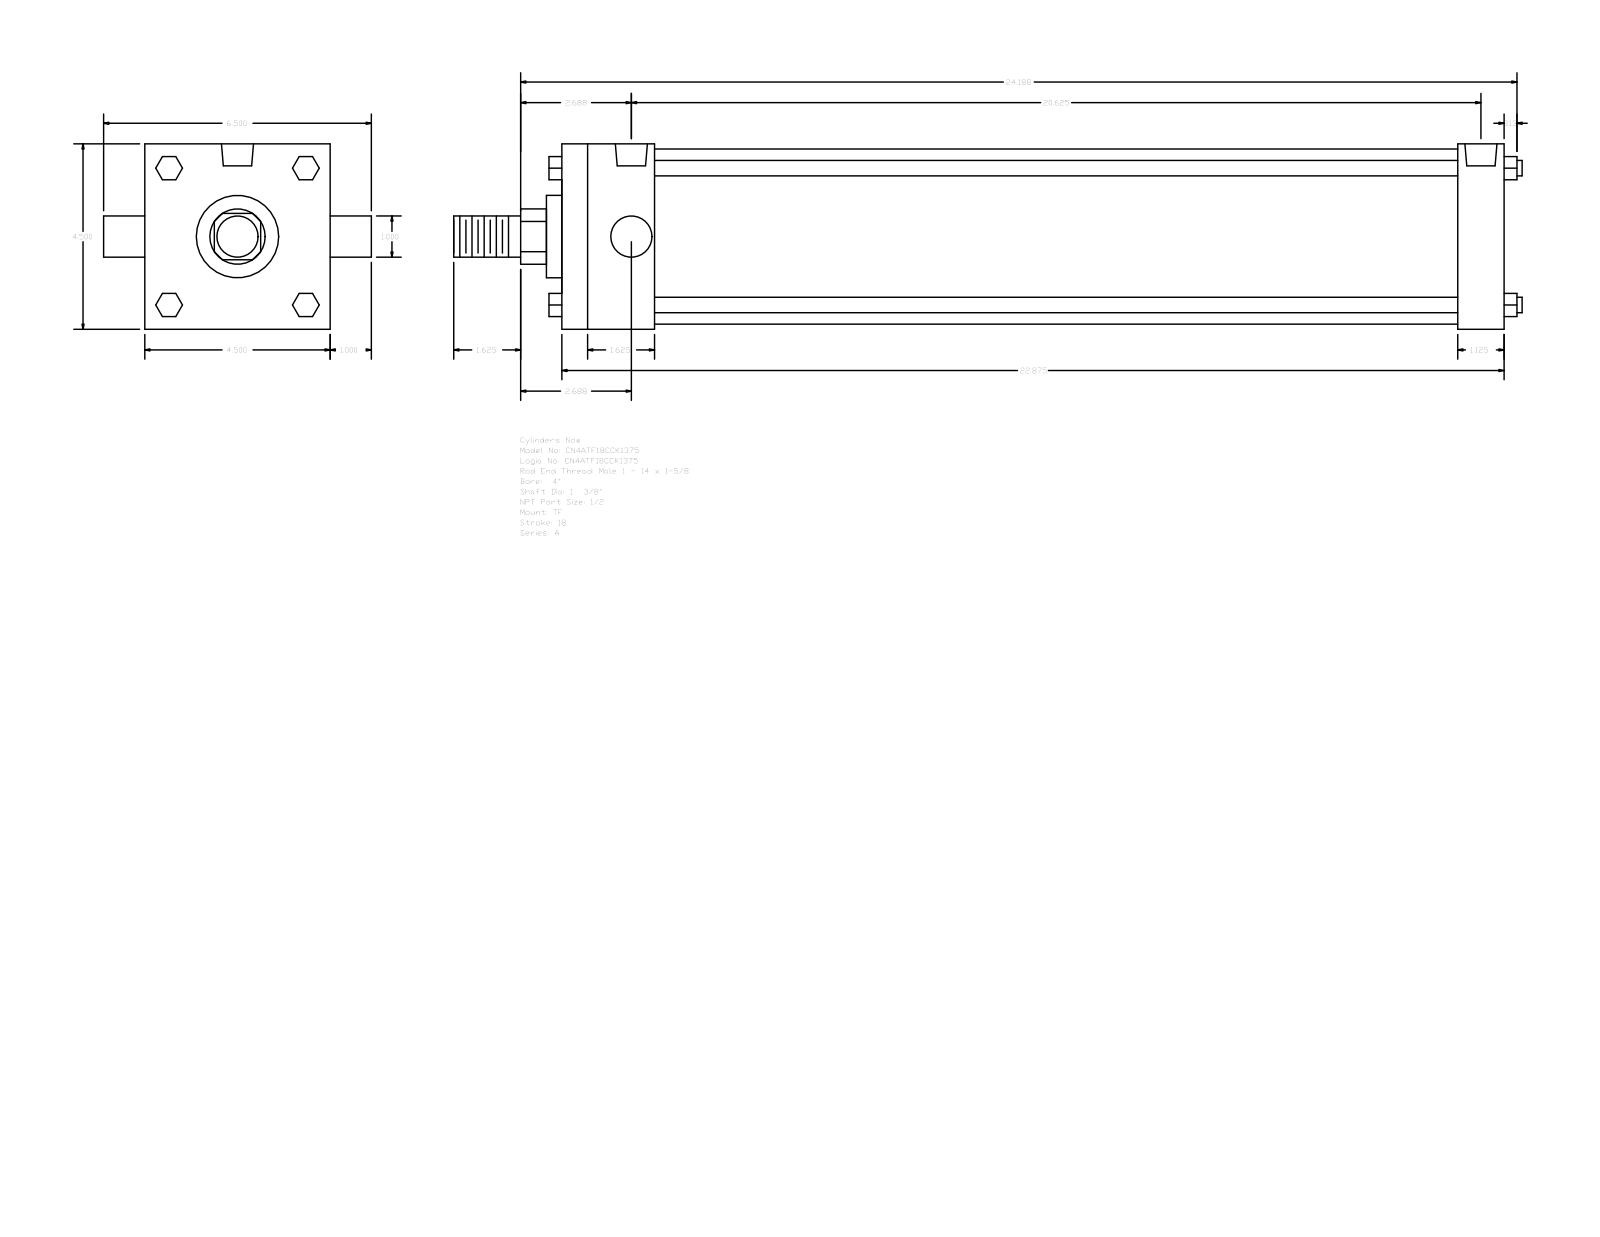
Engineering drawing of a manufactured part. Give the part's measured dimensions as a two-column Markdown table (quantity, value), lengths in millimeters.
| quantity | value |
| --- | --- |
| part name | A_TF__0400_1.375 |
| STEP written by | GSSL Pune (CONFIG_CONTROL_DESIGN) |
| units | millimeters |
| bodies | 0 solids, 120 faces (92 planar, 28 cylindrical, 0 other) |
| overall size | 658.81 × 165.1 × 114.3 |
| round holes (diameter × count) | 8.73 × 3, 19.77 × 2 |
| round bosses / shafts (diameter × count) | 9.53 × 4, 25.4 × 2, 107.95 × 1, 50.8 × 1, 34.92 × 1 |
| partial cylindrical surfaces (radius × count) | 17.06 × 1 |
| main face-to-face distances | 114.3, 581.02, 57.15, 552.45, 28.57, 495.3, 523.87, 66.67, 14.29, 25.4 |
| hole center spacings | 3.18, 520.7, 517.52, 523.88 |
